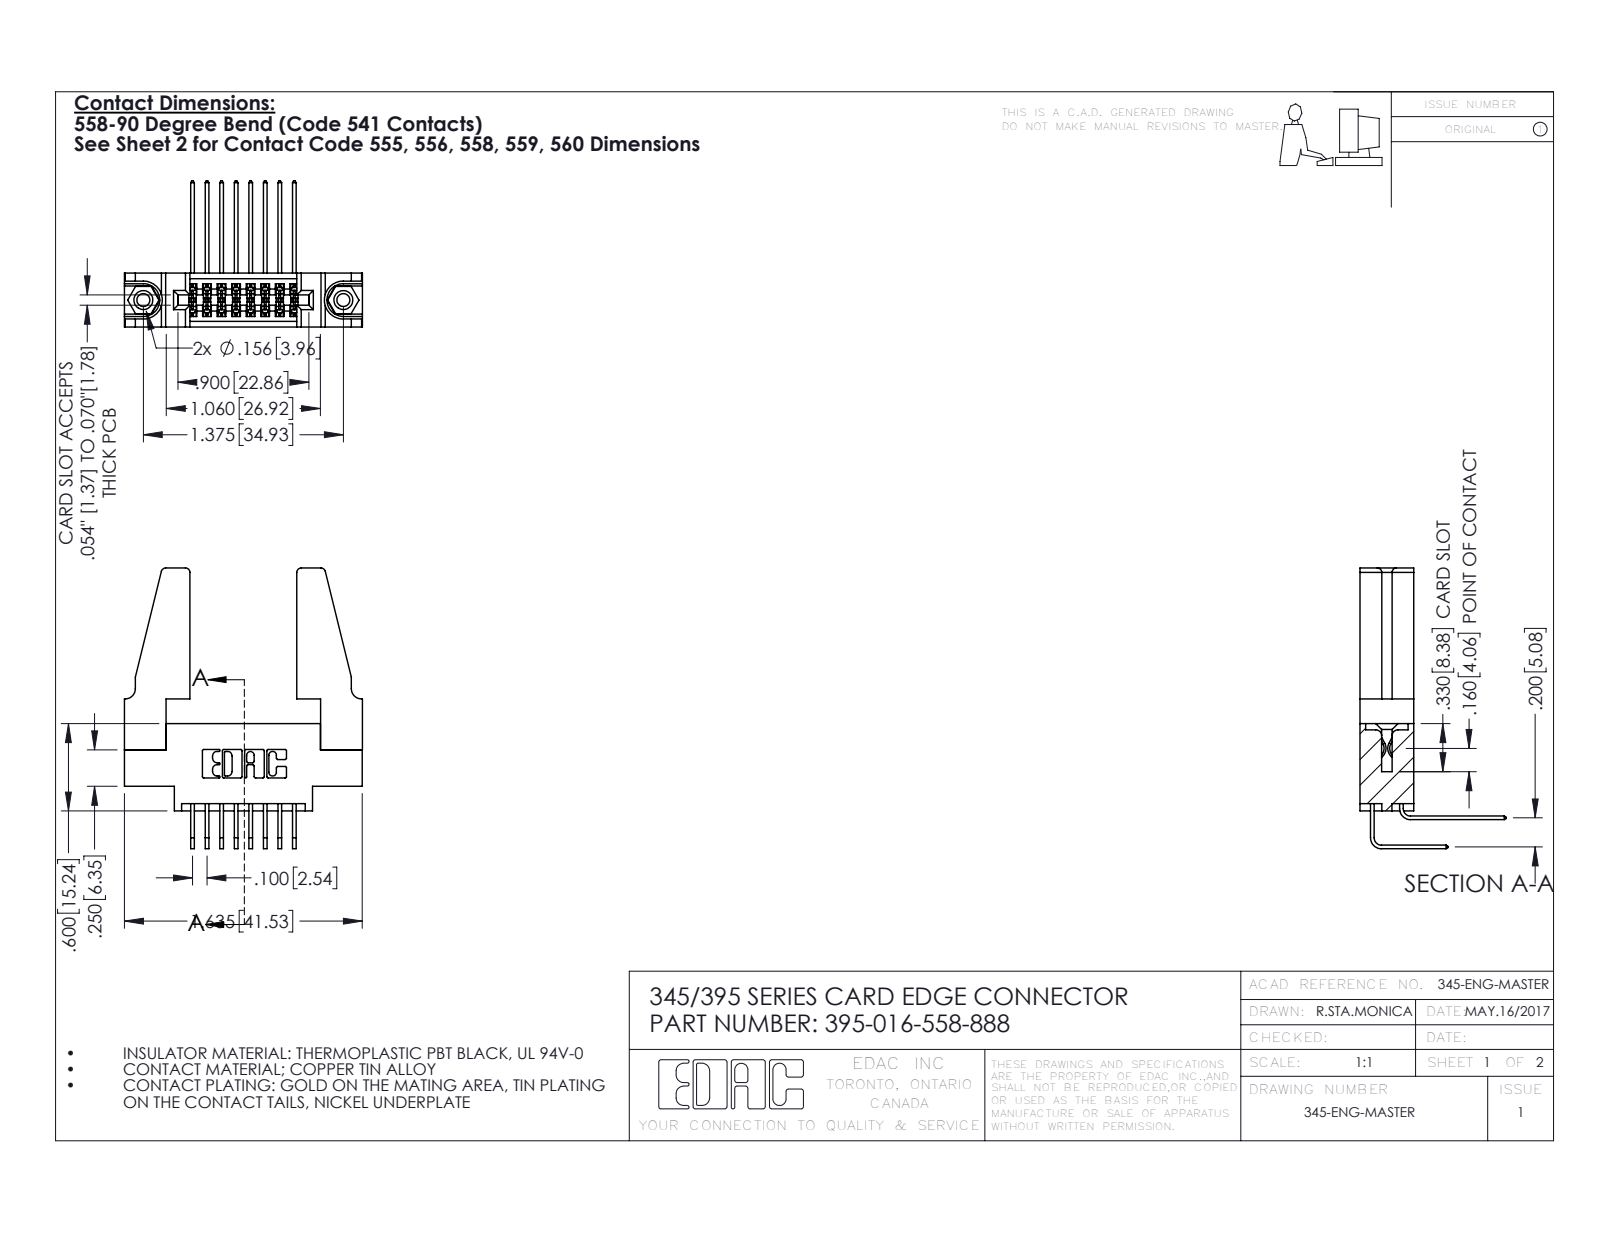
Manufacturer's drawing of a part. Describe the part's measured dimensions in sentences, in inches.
The part is named "345-292-001_558 Tail - 2; 345-292-001_558 559 Tail - 1; 345-220-078_345-220-088; 395-016-558-888 (+2 more)". Its 3-D file was written by "SolidWorks 2016 (CONFIG_CONTROL_DESIGN)". It is 21 solids with 1086 faces: 716 planar, 354 cylindrical and 16 other. Overall it measures 1.929 by 1.636 by 1.005 inches. Its volume is 0.424 cubic inches and its surface area 13.19 square inches. Round holes: 2 of diameter 0.089, 2 of diameter 0.125, 2 of diameter 0.156, 1 of diameter 0.064. Round bosses or shafts: 2 of diameter 0.155. Partial cylindrical surfaces (rounded edges, fillets, slot ends): 25 of radius 0.006, 22 of radius 0.01, 8 of radius 0.03, 6 of radius 0.007, 6 of radius 0.031, 3 of radius 0.026, 2 of radius 0.014, 2 of radius 0.019. The main face-to-face distances are 0.37, 0.072, 0.298, 0.2, 0.098, 0.272, 0.025, 0.225, 0.15, 0.148. The hole center spacings are 0.27, 1.144, 1.375.
